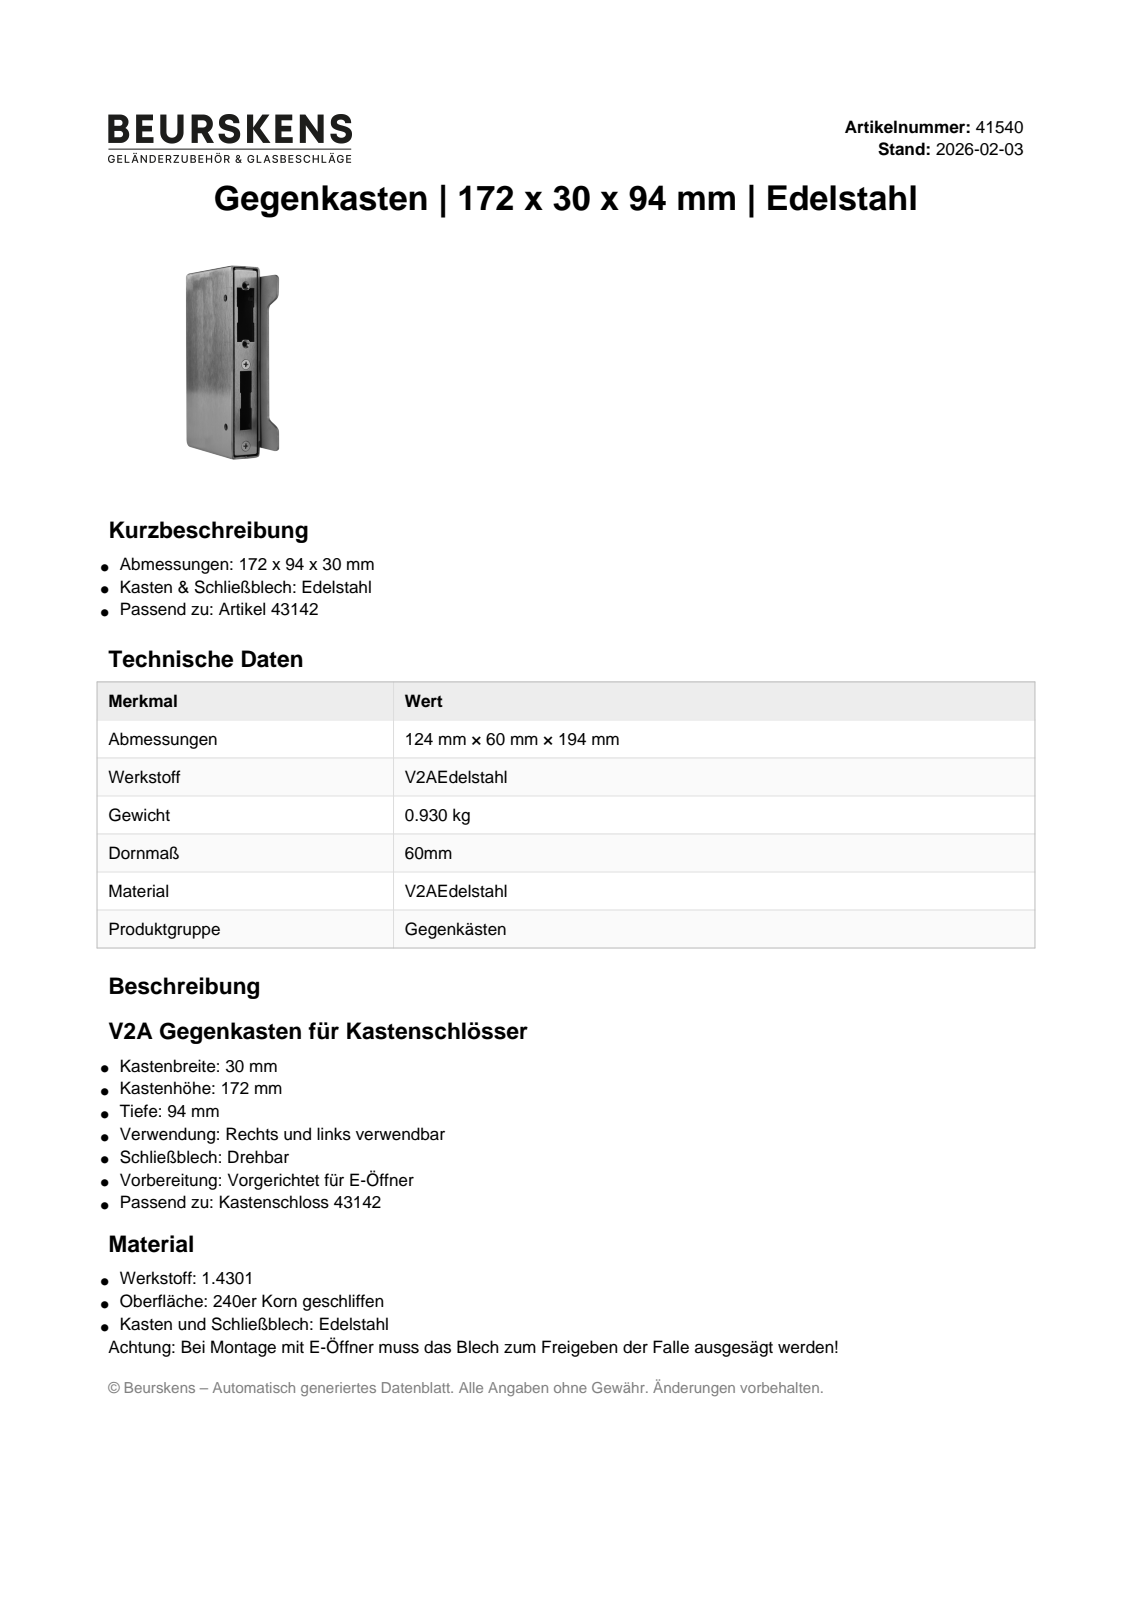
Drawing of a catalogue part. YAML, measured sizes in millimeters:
part_name: "41540"
step_written_by: "Autodesk Inventor 2023 (AUTOMOTIVE_DESIGN)"
units: millimeters
bodies: {solids: 1, faces: 66, planar: 48, cylindrical: 14, other: 4}
overall_size: [172, 94.05, 30.02]
volume: 103440
surface_area: 83655
round_holes:
  - {diameter: 4.2, count: 2}
  - {diameter: 6, count: 2}
partial_cylinders:
  - {radius: 4, count: 8}
face_to_face_distances: [2.5, 27.5, 25, 30, 169.5, 167, 172, 91.5, 94, 8]
hole_center_spacings: [72.75, 115]
